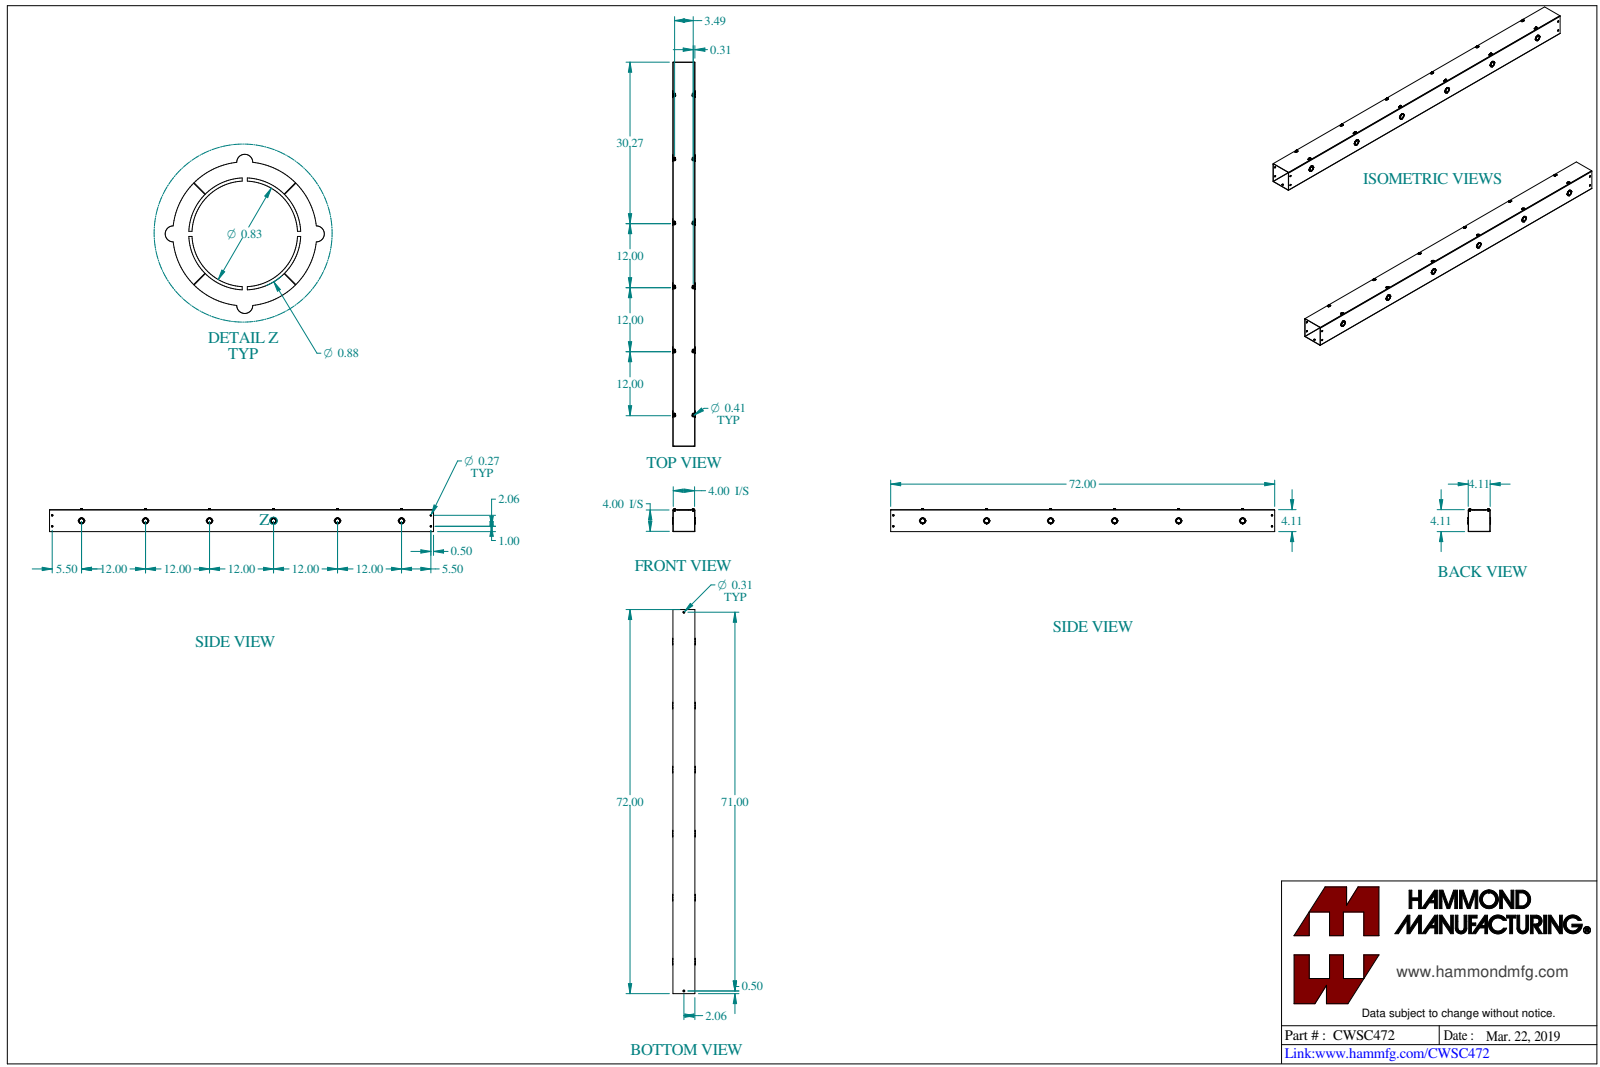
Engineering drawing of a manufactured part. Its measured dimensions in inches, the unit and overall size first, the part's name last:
Units: inches
Overall size (bounding box): 72 × 4.289 × 4.258
Round holes (diameter × count): ⌀0.177 ×12, ⌀0.875 ×6, ⌀0.266 ×4, ⌀0.313 ×2
Round bosses / shafts (diameter × count): ⌀0.375 ×12, ⌀0.19 ×12, ⌀1.125 ×6, ⌀1.125 ×6, ⌀0.825 ×6
Partial cylindrical surfaces — rounded edges, fillets, slot ends (radius × count): R0.062 ×18, R0.125 ×12, R0.203 ×12, R0.063 ×6, R0.029 ×4, R0.086 ×4
Main face-to-face distances: 0.057, 4.057, 4, 4.114, 3.943, 0.114, 0.072, 0.129, 4.129, 4.186
Hole centre spacings: 12, 24, 12.497, 36, 24.252, 3.489, 36.169, 48
Volume: 70.44 in³ · Surface area: 2 469 in²
Bodies: 14 solids, 932 faces (412 planar, 448 cylindrical, 72 other)
Part name (STEP PRODUCT): CWSC472
STEP written by: SolidWorks 2023 (CONFIG_CONTROL_DESIGN)
